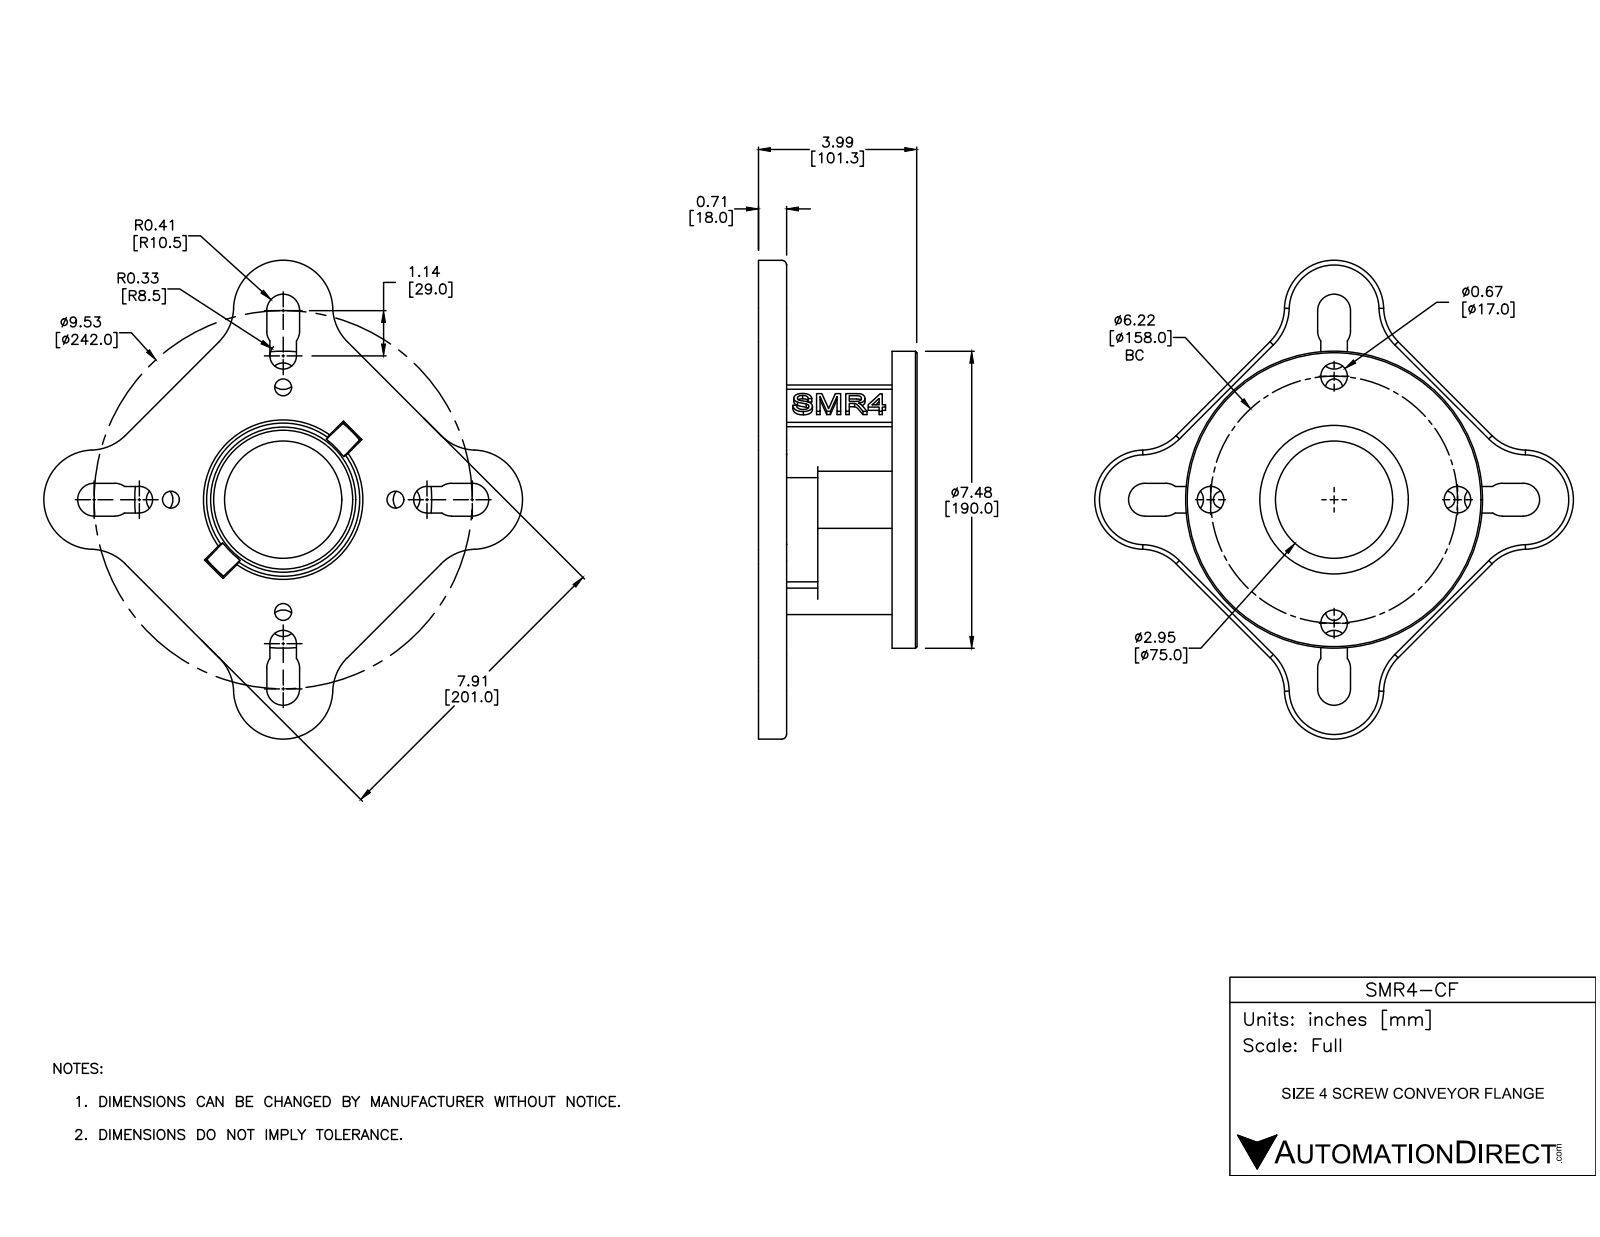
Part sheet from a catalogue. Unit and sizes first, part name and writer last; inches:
Units: inches
Overall size (bounding box): 12.06 × 12.06 × 3.996
Round holes (diameter × count): ⌀0.422 ×4, ⌀0.669 ×4, ⌀2.953 ×1, ⌀3.5 ×1, ⌀3.74 ×1, ⌀3.858 ×1
Round bosses / shafts (diameter × count): ⌀7.48 ×1
Partial cylindrical surfaces — rounded edges, fillets, slot ends (radius × count): R1.25 ×12, R0.394 ×8, R0.413 ×8, R0.118 ×4, R0.335 ×4, R0.591 ×4, R2.067 ×1, R3.248 ×1
Main face-to-face distances: 0.709, 3.287, 3.996, 0.63, 2.657, 3.366, 1.496, 2.5, 1.87, 0.787
Hole centre spacings: 4.204, 0.282, 2.828, 3.11, 4, 4.398, 5.939, 5.657
Volume: 77.86 in³ · Surface area: 292.7 in²
Bodies: 1 solid, 228 faces (99 planar, 83 cylindrical, 46 other)
Part name (STEP PRODUCT): SMR4-CF
STEP written by: SolidWorks 2016 (AUTOMOTIVE_DESIGN)
